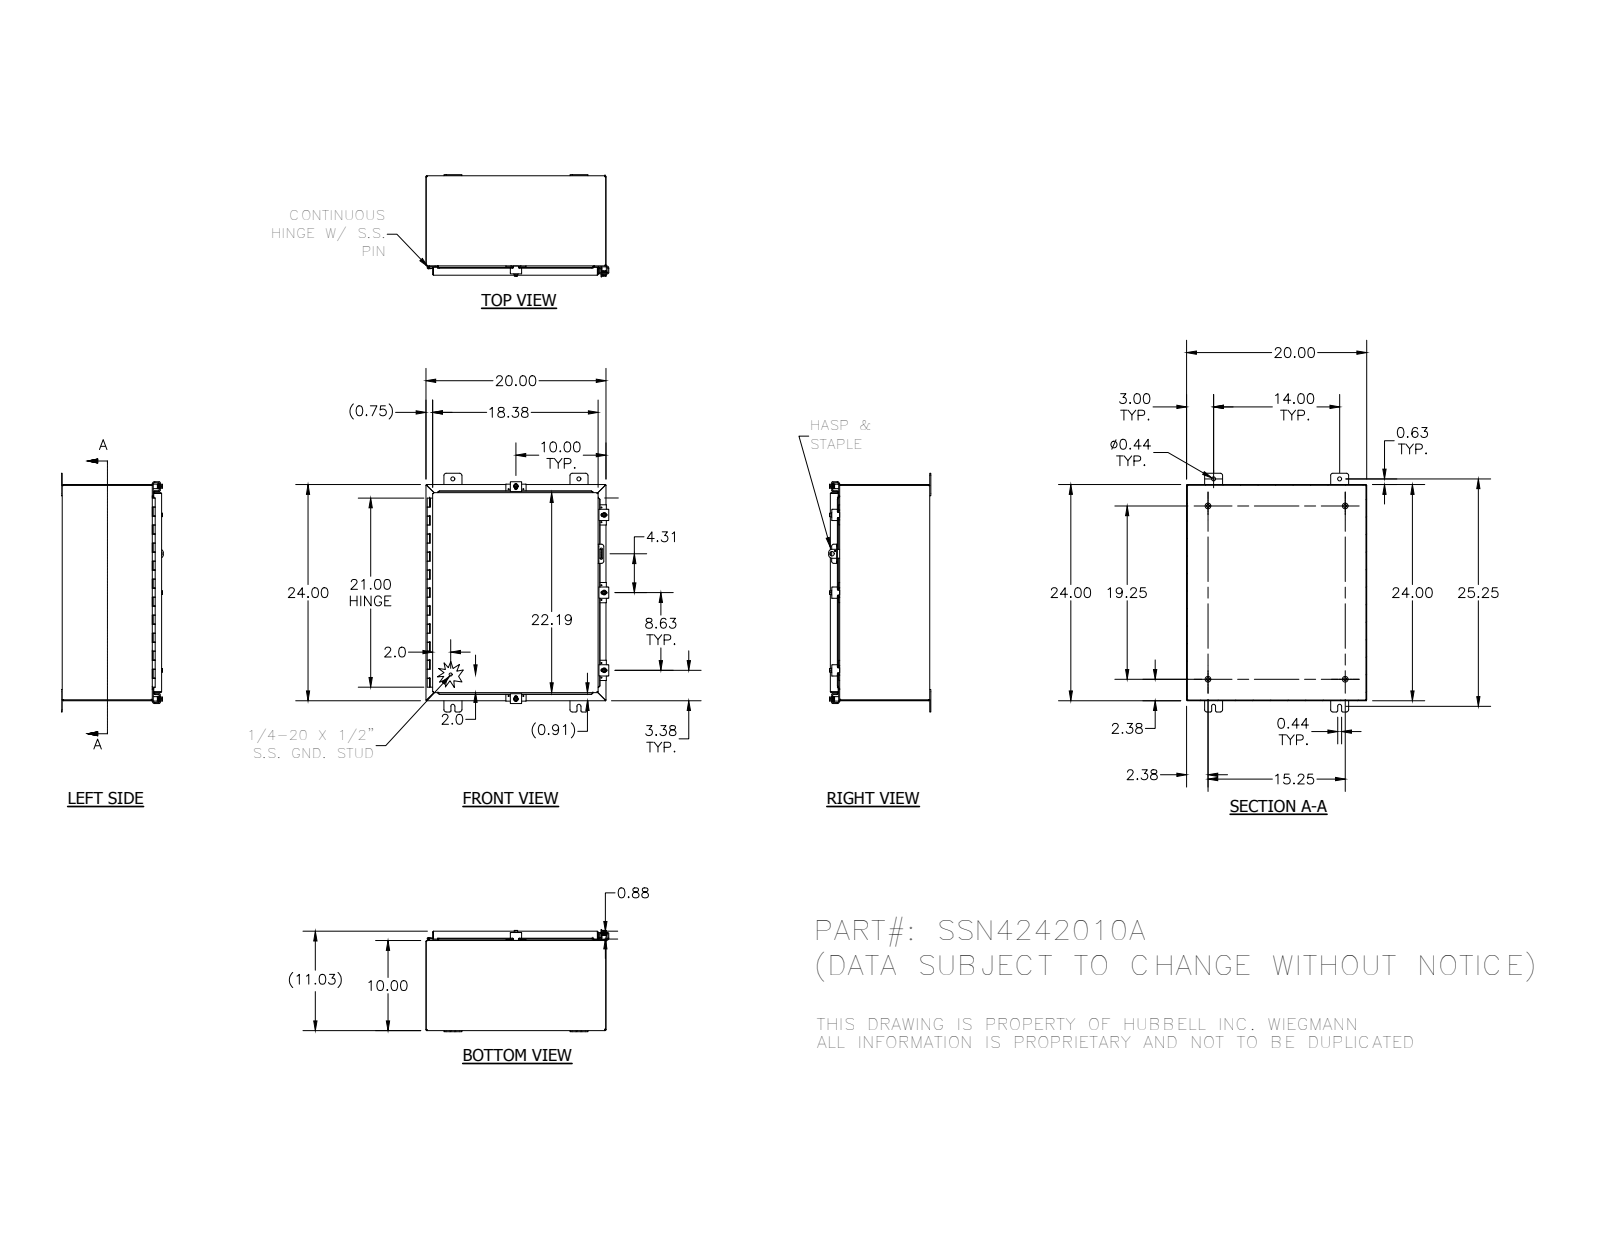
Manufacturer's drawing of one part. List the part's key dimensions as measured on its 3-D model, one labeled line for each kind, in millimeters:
Part name (STEP PRODUCT): 22x18; 38412; 32874-24P; 32912 (+8 more)
STEP written by: SolidWorks 2014 (AUTOMOTIVE_DESIGN)
Units: millimetres
Bodies: 42 solids, 1656 faces (660 planar, 713 cylindrical, 283 other)
Overall size (bounding box): 673.1 × 513.5 × 288.4
Volume: 2 719 000 mm³ · Surface area: 2 814 000 mm²
Round holes (diameter × count): ⌀2.8 ×10, ⌀5.4 ×5, ⌀7.1 ×5, ⌀7.6 ×5, ⌀11.1 ×4, ⌀3.2 ×1, ⌀4 ×1, ⌀12.7 ×1
Round bosses / shafts (diameter × count): ⌀6.4 ×7, ⌀13.2 ×5, ⌀12.7 ×5, ⌀8.9 ×5, ⌀15.9 ×4, ⌀8.4 ×4, ⌀8.6 ×1, ⌀3 ×1
Partial cylindrical surfaces — rounded edges, fillets, slot ends (radius × count): R0.8 ×61, R3.2 ×35, R6.4 ×31, R0.8 ×23, R2.7 ×23, R1.6 ×16, R3.6 ×10, R1.8 ×8
Main face-to-face distances: 1.9, 278.4, 506.1, 276.5, 280.2, 607.7, 508, 504.2, 252.1, 26.2
Hole centre spacings: 22.3, 591.9, 41.3, 198.6, 219.1, 219.1, 239.9, 438.2
